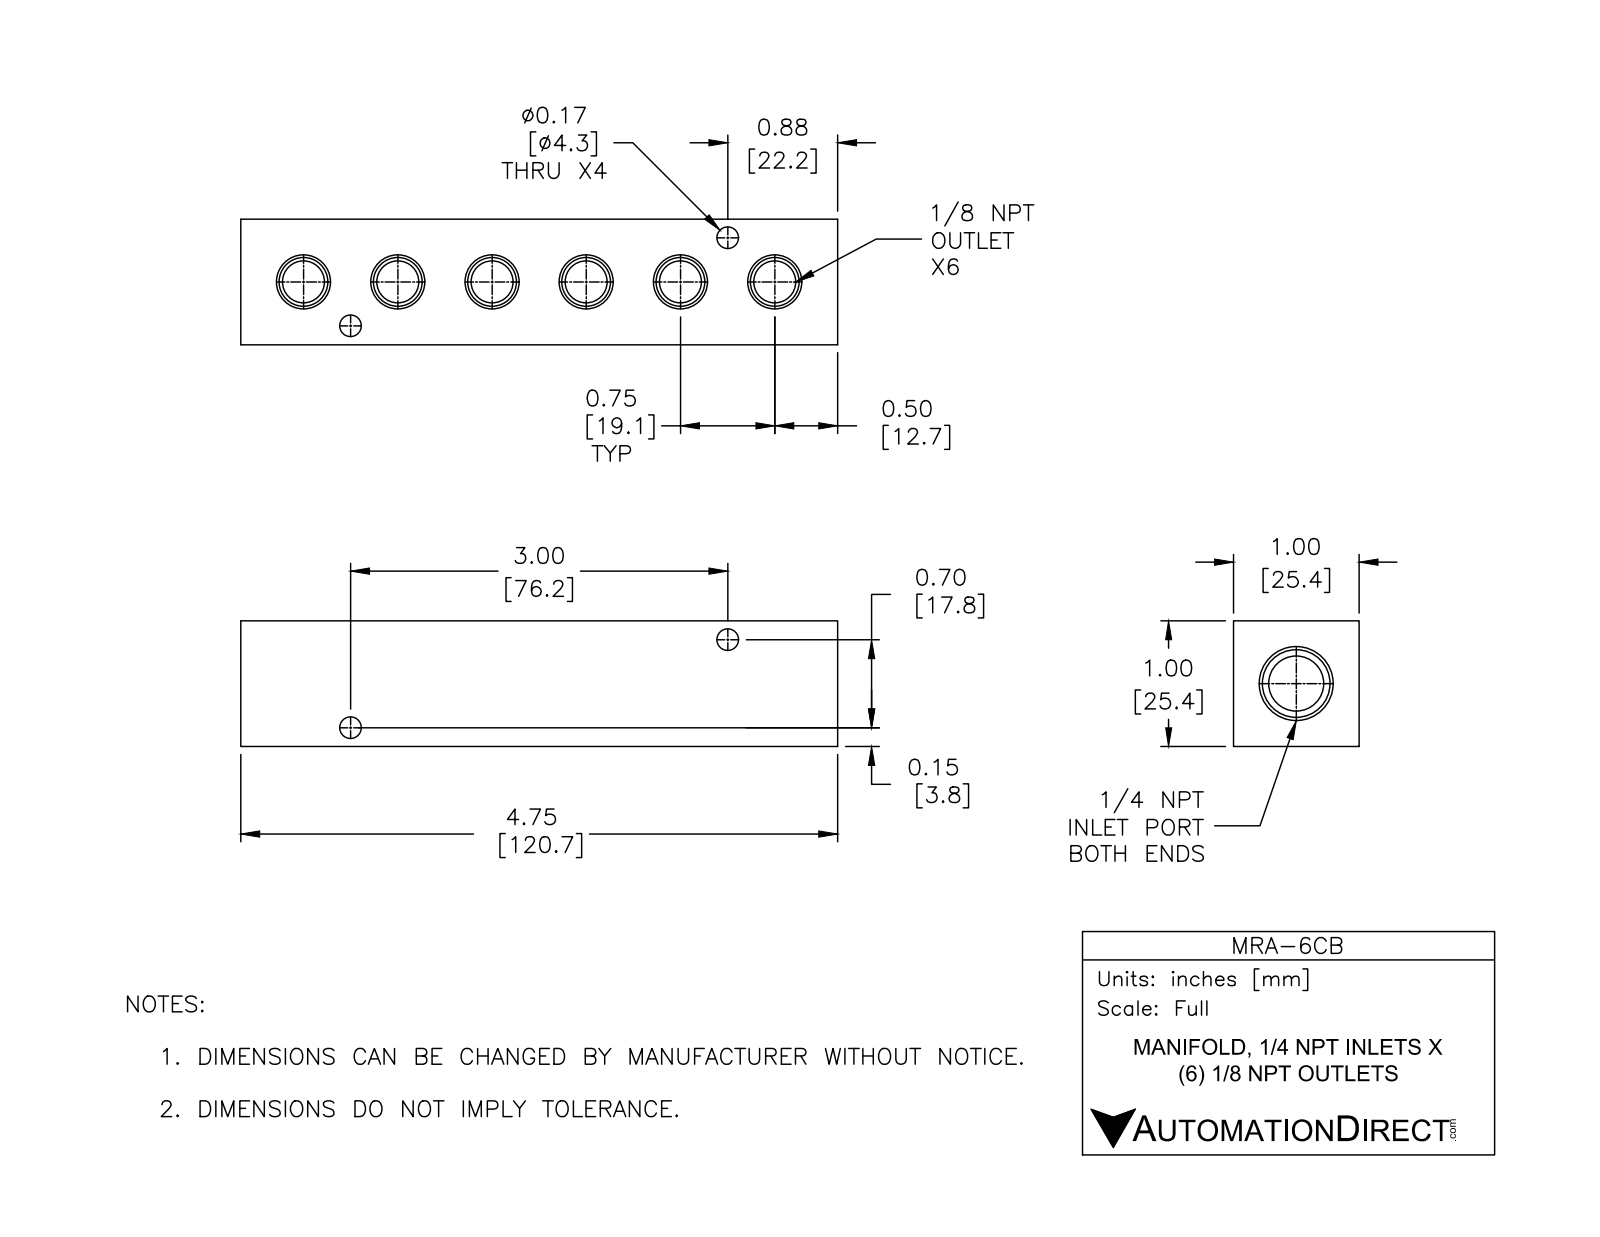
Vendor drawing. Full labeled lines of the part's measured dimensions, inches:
Part name (STEP PRODUCT): MRA-6CB
STEP written by: SolidWorks 2015 (CONFIG_CONTROL_DESIGN)
Units: inches
Bodies: 1 solid, 75 faces (14 planar, 29 cylindrical, 32 other)
Overall size (bounding box): 4.75 × 1 × 1
Volume: 3.68 in³ · Surface area: 30.14 in²
Round holes (diameter × count): ⌀0.17 ×4, ⌀0.332 ×4, ⌀0.438 ×1
Partial cylindrical surfaces — rounded edges, fillets, slot ends (radius × count): R0.166 ×2
Main face-to-face distances: 1, 4.75, 0.73, 0.27, 0.39, 4.36, 3.97
Hole centre spacings: 0.75, 0.513, 1.5, 3.081, 1.178, 1.178, 1.907, 1.907
